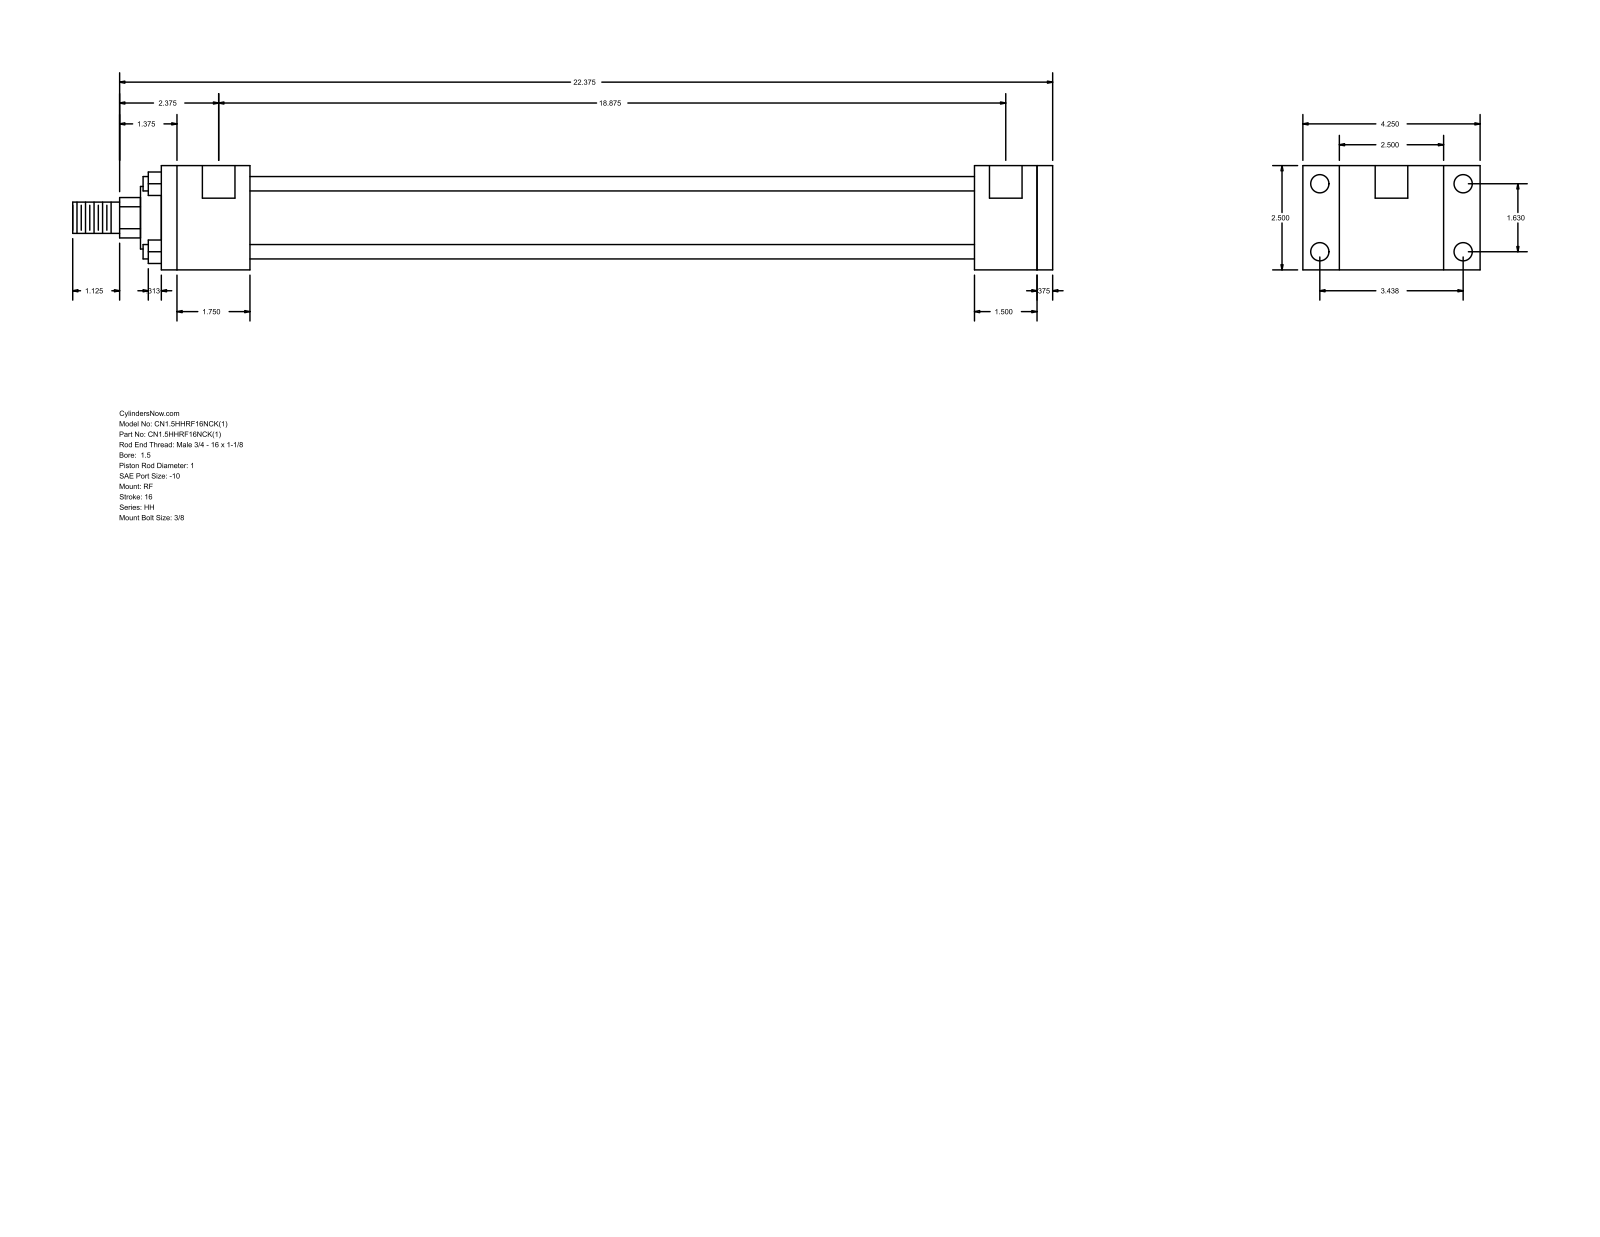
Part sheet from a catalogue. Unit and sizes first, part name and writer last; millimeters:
Units: millimetres
Overall size (bounding box): 596.9 × 107.95 × 63.5
Round holes (diameter × count): ⌀5.56 ×4, ⌀11.13 ×4, ⌀19.84 ×2
Round bosses / shafts (diameter × count): ⌀8.76 ×4, ⌀44.45 ×1, ⌀38.1 ×1, ⌀25.4 ×1, ⌀19.05 ×1
Partial cylindrical surfaces — rounded edges, fillets, slot ends (radius × count): R12.29 ×1
Main face-to-face distances: 63.5, 9.53, 38.1, 441.32, 479.42, 488.95, 47.63, 53.98, 495.3, 533.4
Hole centre spacings: 1.59, 41.4, 87.32, 96.64, 481.01, 482.6, 479.42
Bodies: 0 solids, 92 faces (64 planar, 28 cylindrical, 0 other)
Part name (STEP PRODUCT): HH_RF__0150_1
STEP written by: GSSL Pune (CONFIG_CONTROL_DESIGN)
